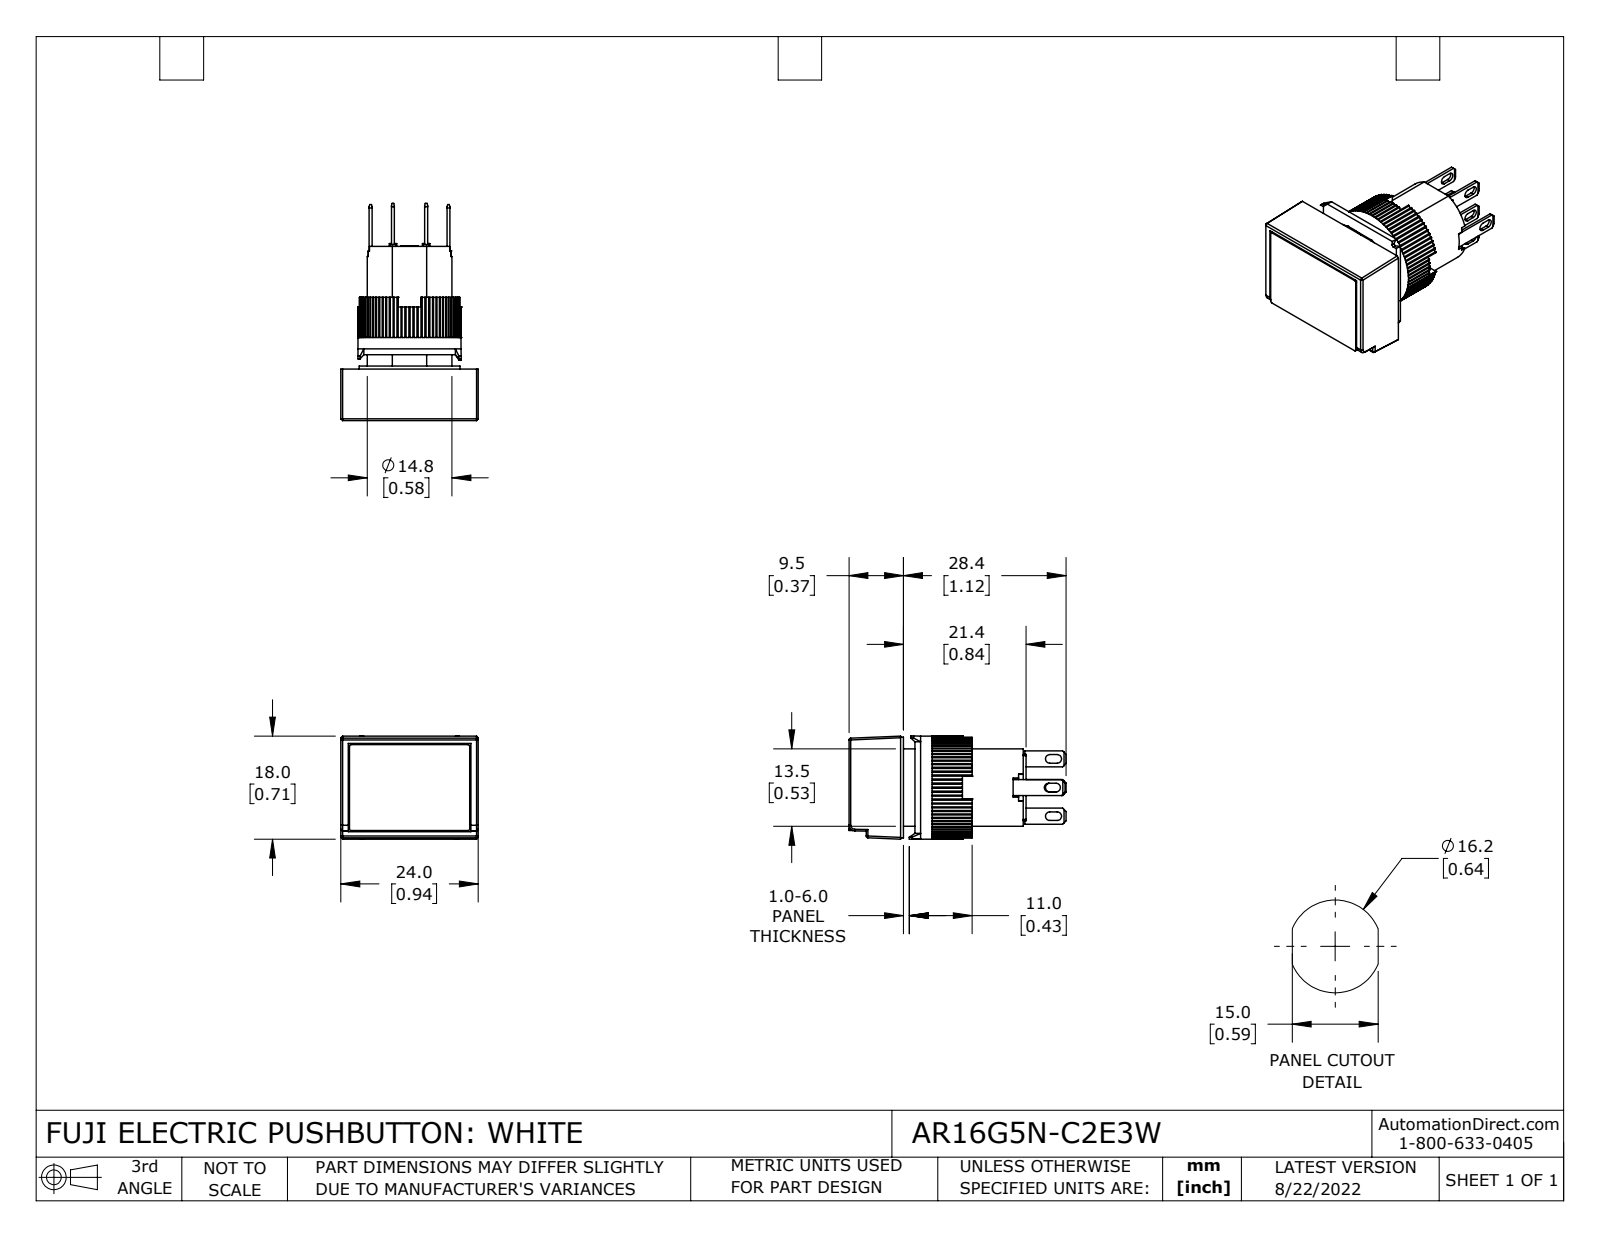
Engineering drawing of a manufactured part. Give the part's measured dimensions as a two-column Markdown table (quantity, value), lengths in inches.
| quantity | value |
| --- | --- |
| part name | AR16G5N-C2E3W |
| STEP written by | SolidWorks 2021 (CONFIG_CONTROL_DESIGN) |
| units | inches |
| bodies | 14 solids, 841 faces (654 planar, 181 cylindrical, 6 other) |
| overall size | 1.492 × 0.945 × 0.709 |
| volume | 0.448 in³ |
| surface area | 9.503 in² |
| round holes (diameter × count) | 0.543 × 1, 0.583 × 1 |
| round bosses / shafts (diameter × count) | 0.709 × 1, 0.693 × 1 |
| partial cylindrical surfaces (radius × count) | 0.01 × 80, 0.008 × 12, 0.03 × 8, 0.012 × 6, 0.039 × 1 |
| main face-to-face distances | 0.213, 0.354, 0.142, 0.35, 0.492, 0.138, 0.02, 0.843, 0.059, 0.453 |
